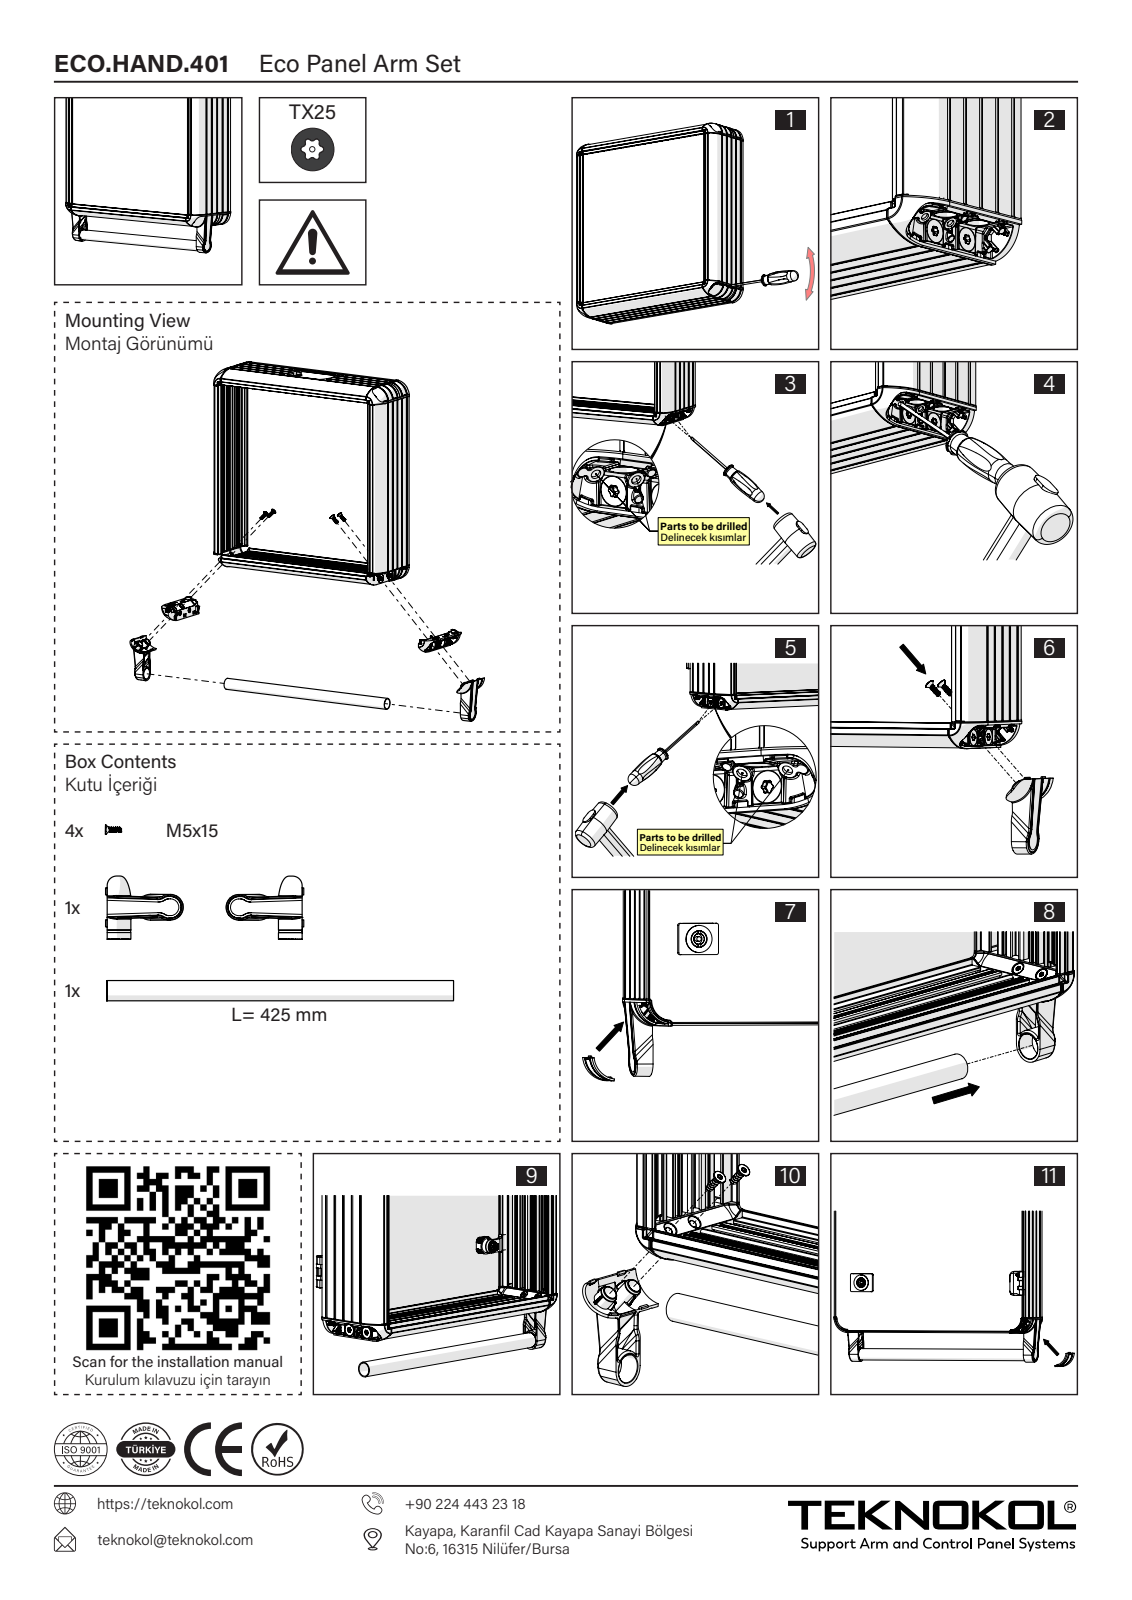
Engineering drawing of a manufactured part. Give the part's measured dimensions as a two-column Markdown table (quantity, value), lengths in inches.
| quantity | value |
| --- | --- |
| part name | ECO.HAND.401 |
| STEP written by | SolidWorks 2023 (AUTOMOTIVE_DESIGN) |
| units | inches |
| bodies | 11 solids, 869 faces (196 planar, 286 cylindrical, 387 other) |
| overall size | 16.732 × 3.179 × 0.934 |
| volume | 3.258 in³ |
| surface area | 119.4 in² |
| round holes (diameter × count) | 0.197 × 4, 0.354 × 4, 0.748 × 2, 0.669 × 1 |
| round bosses / shafts (diameter × count) | 0.354 × 4, 0.11 × 4, 0.748 × 1 |
| partial cylindrical surfaces (radius × count) | 0.012 × 68, 0.016 × 24, 0.068 × 16, 0.059 × 14, 0.039 × 12, 0.118 × 12, 0.047 × 8, 0.054 × 4 |
| main face-to-face distances | 0.098, 0.09, 0.018, 0.453, 0.099, 0.019, 0.059, 0.472, 0.472, 0.019 |
| hole center spacings | 0.945, 1.085 |
